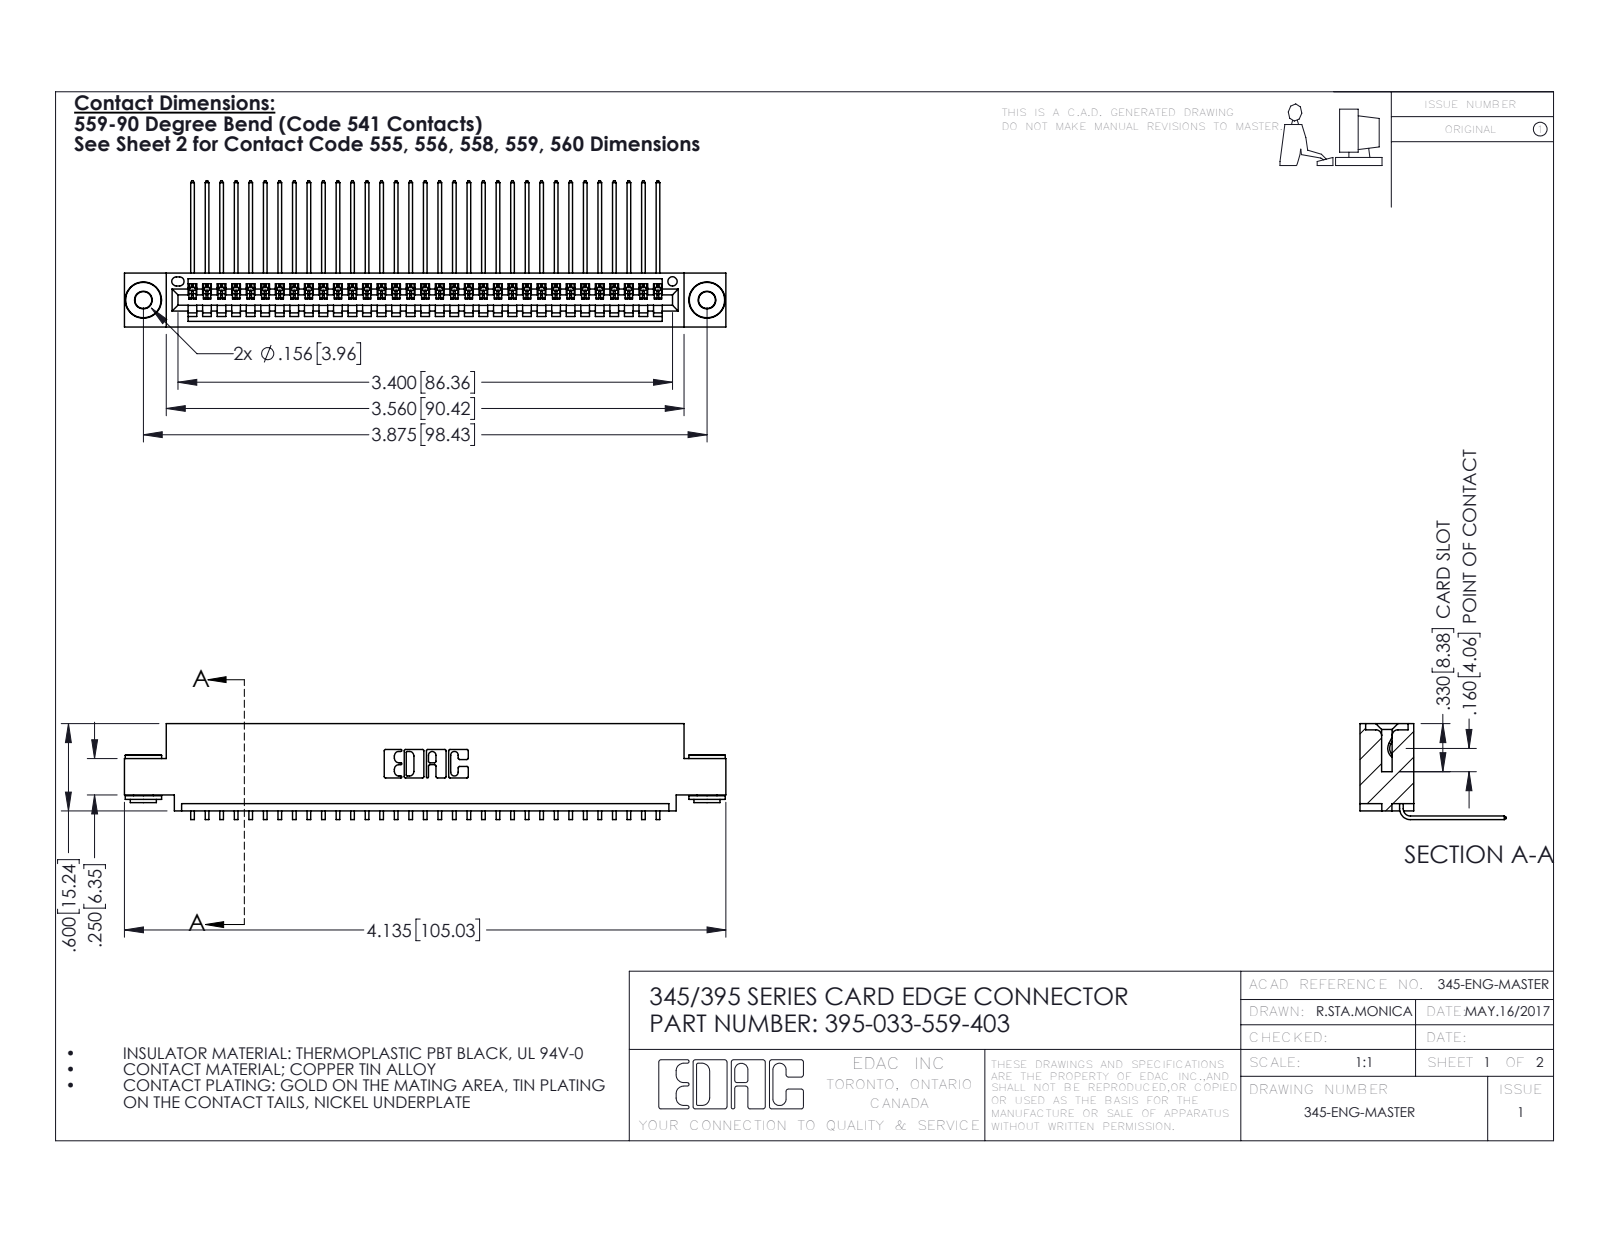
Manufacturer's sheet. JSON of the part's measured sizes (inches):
{"part_name": "345-292-001_558 559 Tail - 1; 345 Part_0.110 Offset - 0.156 Dia-TH; 395-033-559-403; 345-250-002_345-250-002-102", "step_written_by": "SolidWorks 2016 (CONFIG_CONTROL_DESIGN)", "units": "inches", "bodies": {"solids": 36, "faces": 2148, "planar": 1480, "cylindrical": 660, "other": 8}, "overall_size": [4.135, 1.005, 0.659], "volume_in3": 0.608, "surface_area_in2": 21.78, "round_holes": [[0.116, 2], [0.156, 2], [0.064, 1]], "round_bosses_or_shafts": [[0.25, 2], [0.18, 2], [0.136, 2]], "partial_cylinders_radius": [[0.006, 66], [0.01, 22], [0.007, 6], [0.031, 6], [0.026, 3], [0.031, 2], [0.04, 2], [0.014, 1]], "face_to_face_distances": [0.072, 0.298, 0.37, 0.2, 0.025, 0.098, 0.272, 0.225, 0.149, 0.072], "hole_center_spacings": [0.27, 3.64, 3.875]}
